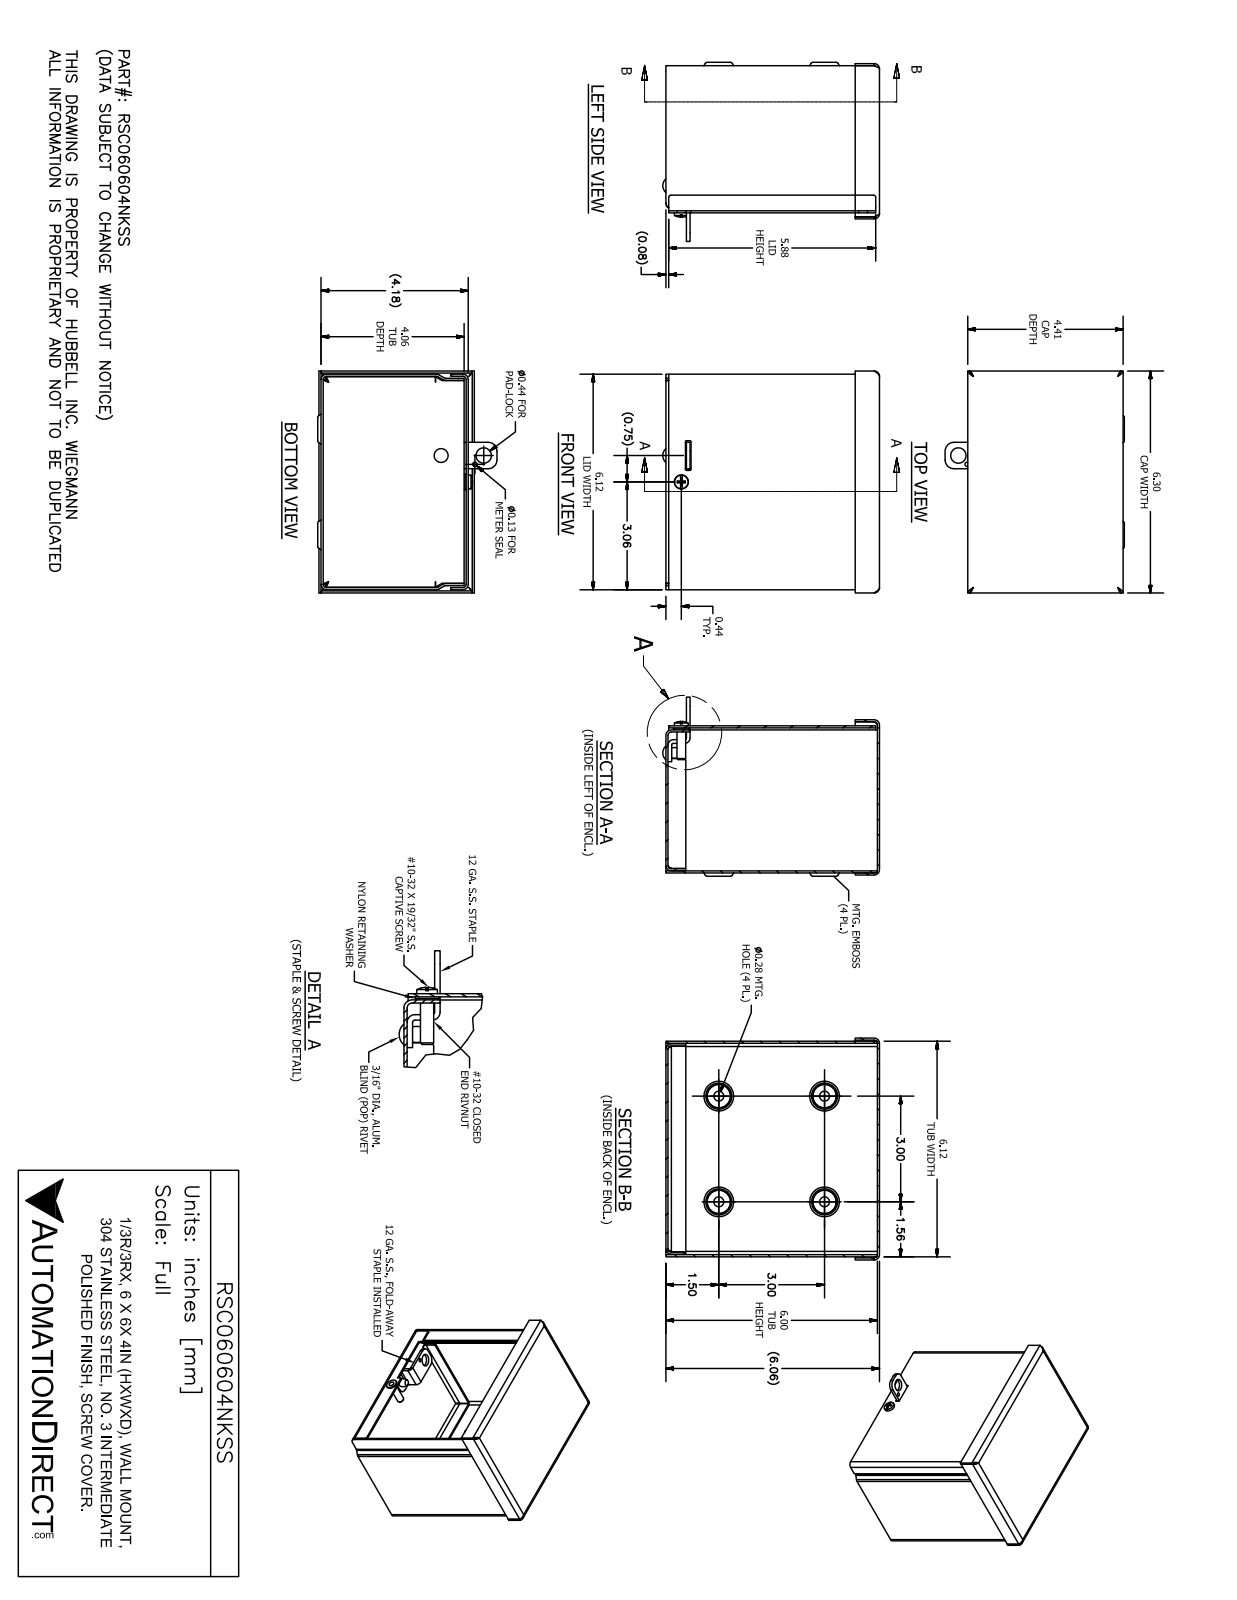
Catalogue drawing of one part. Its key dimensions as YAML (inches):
part_name: "RSC060604NKSS"
step_written_by: "SolidWorks 2017 (AUTOMOTIVE_DESIGN)"
units: inches
bodies: {solids: 9, faces: 292, planar: 149, cylindrical: 79, other: 64}
overall_size: [6.299, 6.149, 5.084]
volume: 11.85
surface_area: 407.8
round_holes:
  - {diameter: 0.281, count: 4}
  - {diameter: 0.25, count: 2}
  - {diameter: 0.125, count: 1}
  - {diameter: 0.156, count: 1}
  - {diameter: 0.196, count: 1}
  - {diameter: 0.198, count: 1}
  - {diameter: 0.201, count: 1}
  - {diameter: 0.257, count: 1}
  - {diameter: 0.278, count: 1}
  - {diameter: 0.437, count: 1}
round_bosses_or_shafts:
  - {diameter: 0.453, count: 1}
  - {diameter: 0.406, count: 1}
  - {diameter: 0.248, count: 1}
  - {diameter: 0.187, count: 1}
  - {diameter: 0.167, count: 1}
partial_cylinders:
  - {radius: 0.094, count: 16}
  - {radius: 0.153, count: 16}
  - {radius: 0.031, count: 6}
  - {radius: 0.25, count: 4}
  - {radius: 0.063, count: 3}
  - {radius: 0.047, count: 2}
  - {radius: 0.05, count: 2}
  - {radius: 0.062, count: 2}
face_to_face_distances: [0.059, 4.117, 6, 6.059, 4.176, 4.058, 5.941, 6.118, 0.117, 0.059]
hole_center_spacings: [3, 1.838, 1.856, 4.243, 4.331, 4.36, 0.354, 0.99]
